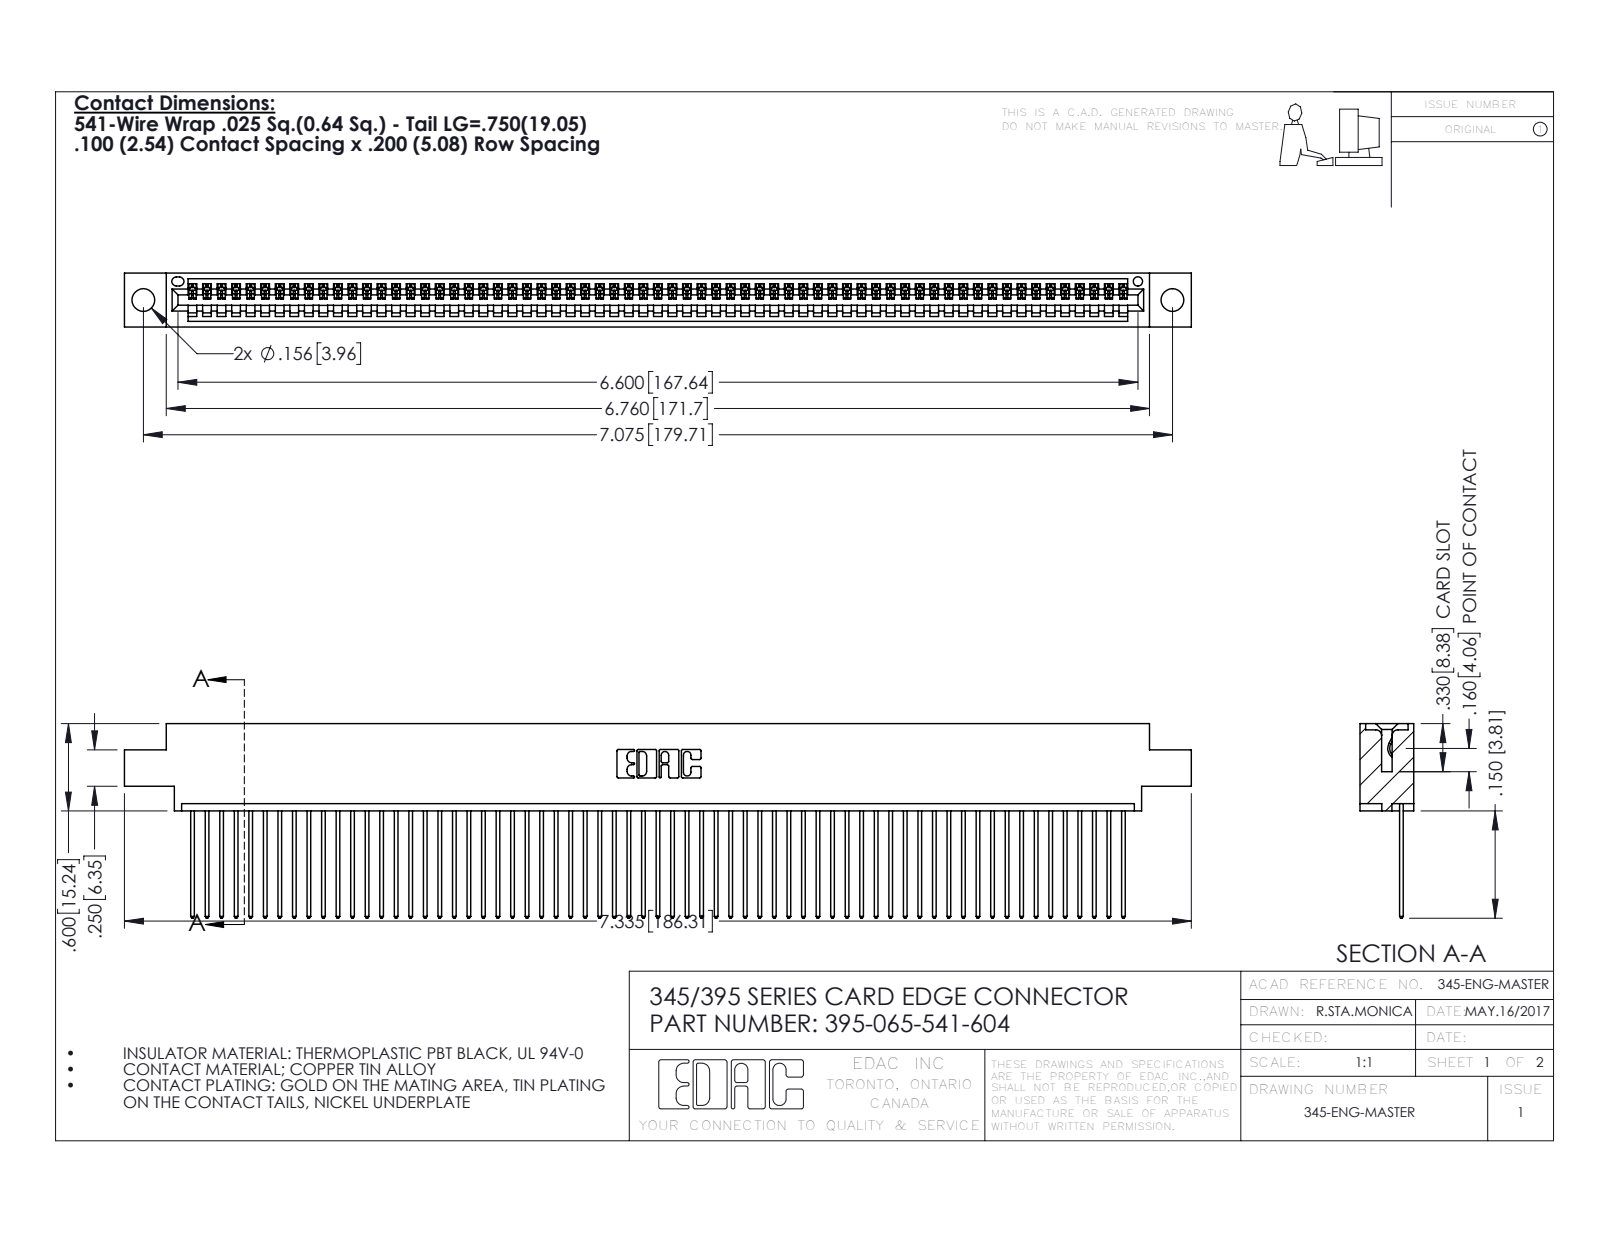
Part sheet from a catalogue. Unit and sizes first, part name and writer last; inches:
Units: inches
Overall size (bounding box): 7.335 × 1.337 × 0.37
Round holes (diameter × count): ⌀0.156 ×2, ⌀0.064 ×1
Partial cylindrical surfaces — rounded edges, fillets, slot ends (radius × count): R0.006 ×130, R0.01 ×130, R0.01 ×22, R0.007 ×6, R0.031 ×6, R0.026 ×3, R0.031 ×2, R0.04 ×2
Main face-to-face distances: 0.072, 0.298, 0.098, 0.272, 0.025, 0.37, 0.2, 0.225, 0.175, 0.149
Hole centre spacings: 0.27, 6.839, 7.075
Volume: 1.092 in³ · Surface area: 39.21 in²
Bodies: 66 solids, 3900 faces (2684 planar, 1216 cylindrical, 0 other)
Part name (STEP PRODUCT): 345 Part_0.170 Offset - 0.156 Dia-TH; 345-292-001_345-293-141; 395-065-541-604
STEP written by: SolidWorks 2016 (CONFIG_CONTROL_DESIGN)
